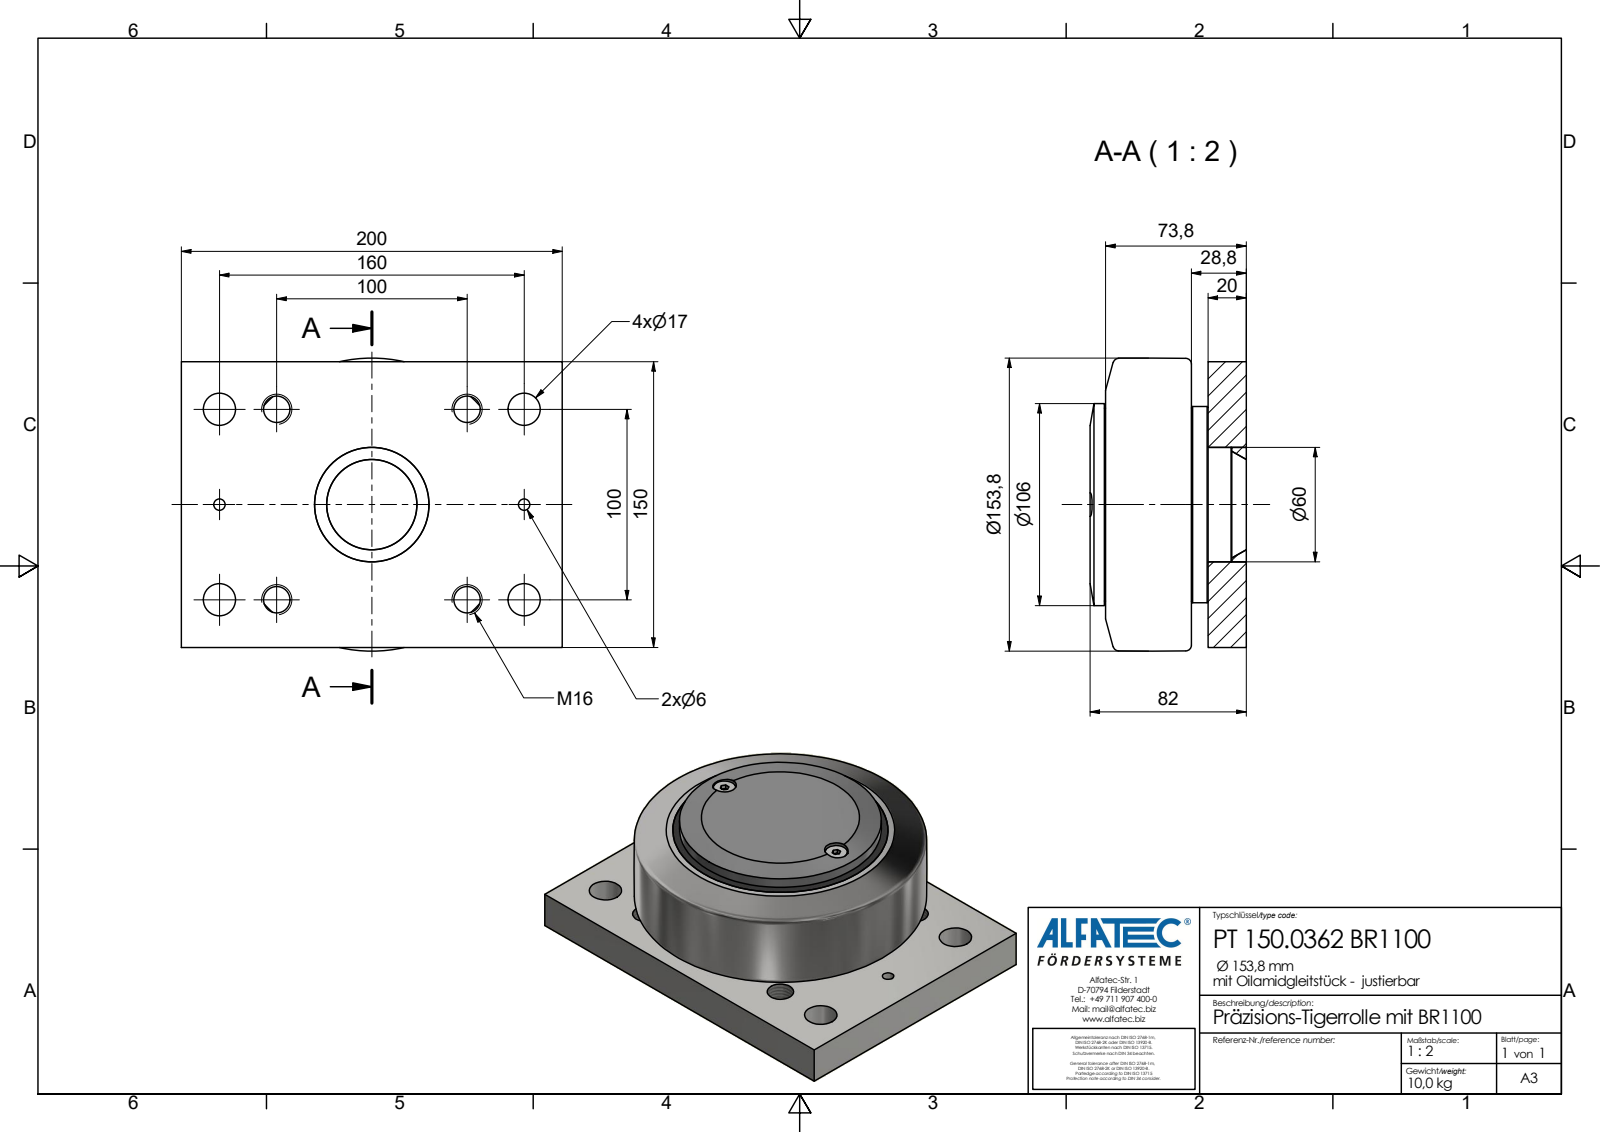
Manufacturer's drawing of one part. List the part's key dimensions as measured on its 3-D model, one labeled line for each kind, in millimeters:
Part name (STEP PRODUCT): PT 150.0362 BR1100_Kontur
STEP written by: Autodesk Inventor 2020 (AP242_MANAGED_MODEL_BASED_3D_ENGINEERING_MIM_LF)
Units: millimetres
Bodies: 1 solid, 54 faces (27 planar, 18 cylindrical, 9 other)
Overall size (bounding box): 200 × 153.8 × 82
Volume: 1 526 000 mm³ · Surface area: 126 032 mm²
Round holes (diameter × count): ⌀13.84 ×4, ⌀17 ×4, ⌀6 ×2, ⌀12.4 ×2
Round bosses / shafts (diameter × count): ⌀11.7 ×2, ⌀106 ×1, ⌀103 ×1, ⌀101.4 ×1, ⌀101.2 ×1
Main face-to-face distances: 20, 28.8, 8.8, 82, 62, 53.2, 150, 73.8, 53.8, 45
Hole centre spacings: 100, 30, 50, 50.72, 58.31, 63.11, 104.27, 104.4
